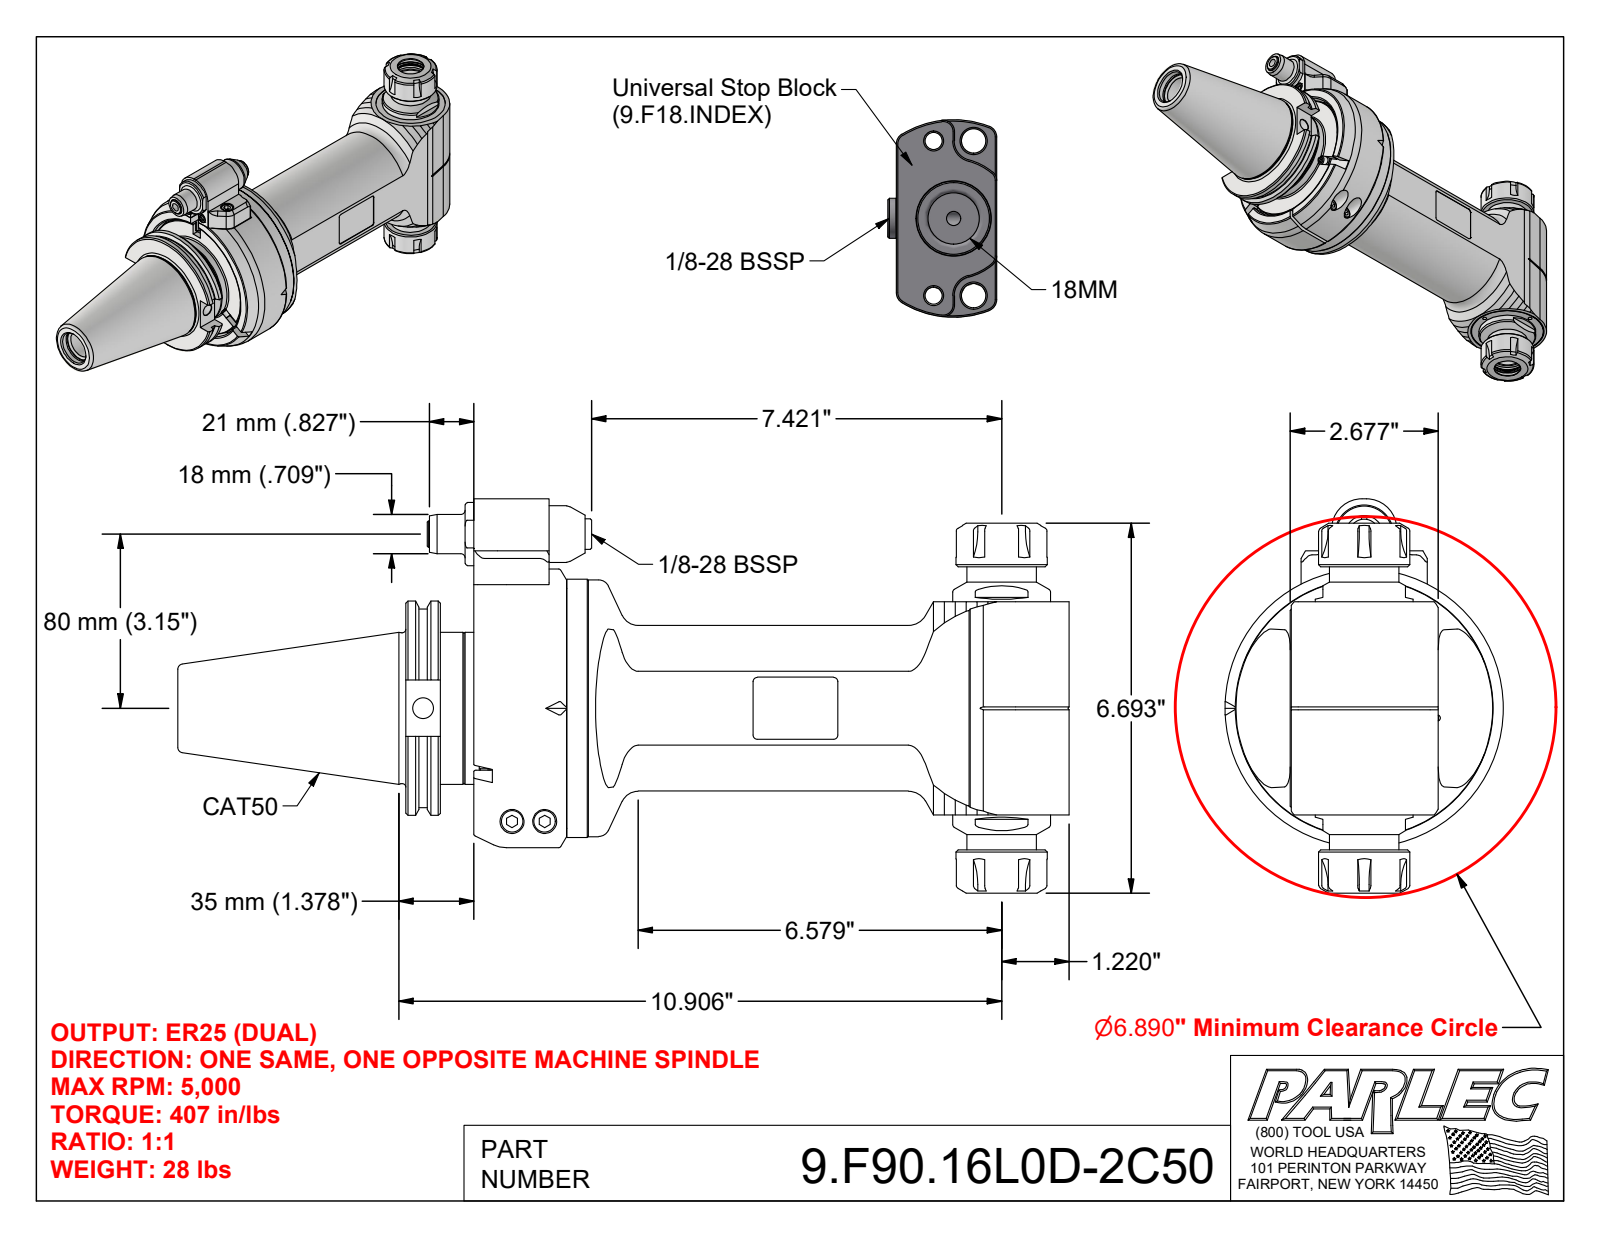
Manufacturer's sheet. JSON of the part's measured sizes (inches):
{"part_name": "9.F90.16L0D-2C50; 9_F90_16L_2U0; 9_GA2_458_2 (Type 2, Cat50, 80mm)", "step_written_by": "Autodesk Inventor 2022 (AUTOMOTIVE_DESIGN)", "units": "inches", "bodies": {"solids": 6, "faces": 666, "planar": 283, "cylindrical": 164, "other": 219}, "overall_size": [16.126, 7.136, 5.039], "volume_in3": 133.8, "surface_area_in2": 385, "round_holes": [[0.413, 20], [0.126, 4], [0.197, 4], [0.102, 2], [0.165, 2], [0.209, 2], [0.315, 2], [0.409, 2], [0.433, 2], [0.492, 2], [1.063, 2], [0.098, 1]], "round_bosses_or_shafts": [[0.394, 4], [0.236, 4], [0.709, 2], [0.098, 2], [5.039, 1], [4.669, 1], [4.646, 1], [3.898, 1]], "partial_cylinders_radius": [[0.079, 12], [0.984, 12], [0.157, 4], [0.016, 2], [0.02, 2], [0.039, 2], [0.138, 2], [0.315, 2]], "face_to_face_distances": [1.378, 2.677, 1.398, 0.236, 0.197, 1.339, 1.575, 0.039, 0.02, 2.281], "hole_center_spacings": [2.603, 2.215, 1.841, 3.645, 0.512, 1.785, 2.94, 1.015]}
